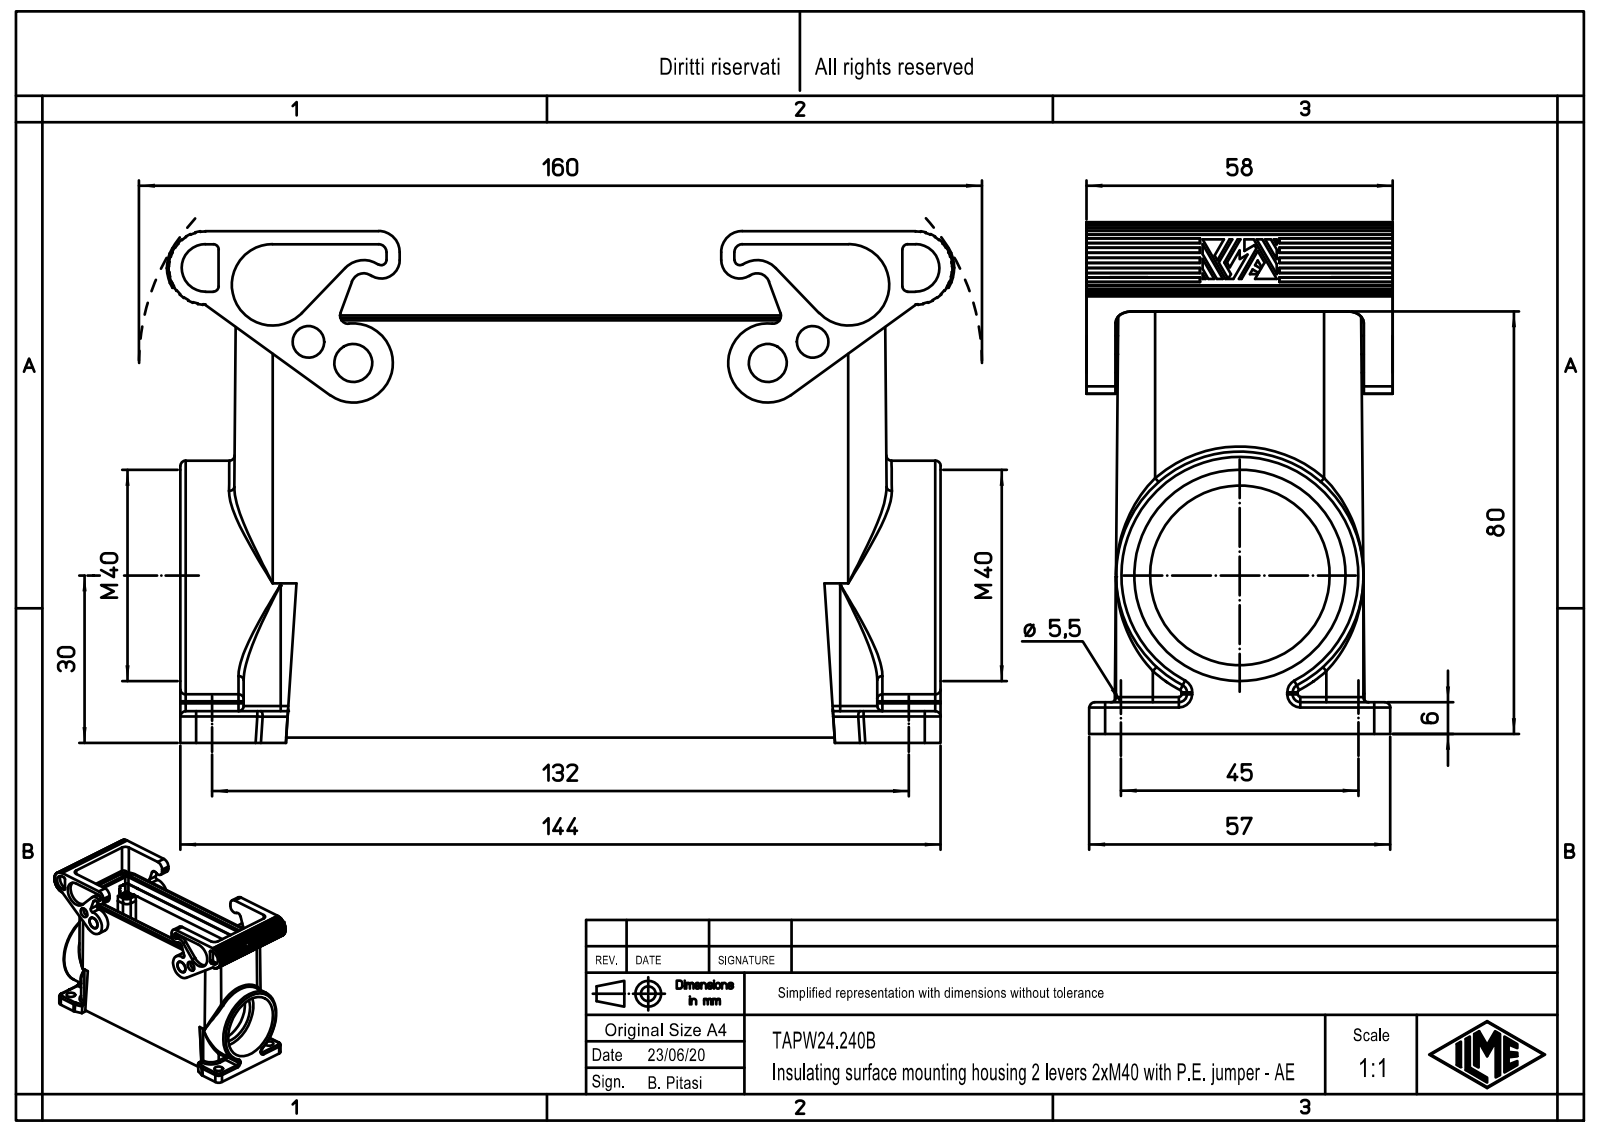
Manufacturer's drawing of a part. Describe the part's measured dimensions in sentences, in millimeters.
The part is named "TAPW24.240B". Its 3-D file was written by "Creo Elements/Direct Modeling 20.1B 02-Apr-2019 (C) Parametric Technology GmbH (AUTOMOTIVE_DESIGN)". It is 1 solid with 975 faces: 561 planar, 282 cylindrical and 132 other. Overall it measures 149.1 by 96.9 by 58 millimeters. Its volume is 214 105 cubic millimeters and its surface area 86 574 square millimeters. Round holes: 4 of diameter 3, 4 of diameter 3.5, 4 of diameter 5.5, 2 of diameter 6, 2 of diameter 10, 1 of diameter 34, 1 of diameter 40. Round bosses or shafts: 4 of diameter 4.8, 2 of diameter 7, 1 of diameter 46.87. Partial cylindrical surfaces (rounded edges, fillets, slot ends): 22 of radius 1, 20 of radius 1.5, 12 of radius 3, 6 of radius 3.5, 6 of radius 7, 4 of radius 0.5, 4 of radius 1.3, 4 of radius 1.6. The main face-to-face distances are 40.6, 5.5, 6.5, 1, 52.5, 8.75, 2.5, 55.5, 40.4, 12.1. The hole center spacings are 16.64, 38.63, 118.34, 123.37, 9.39, 27, 45, 87.09.
